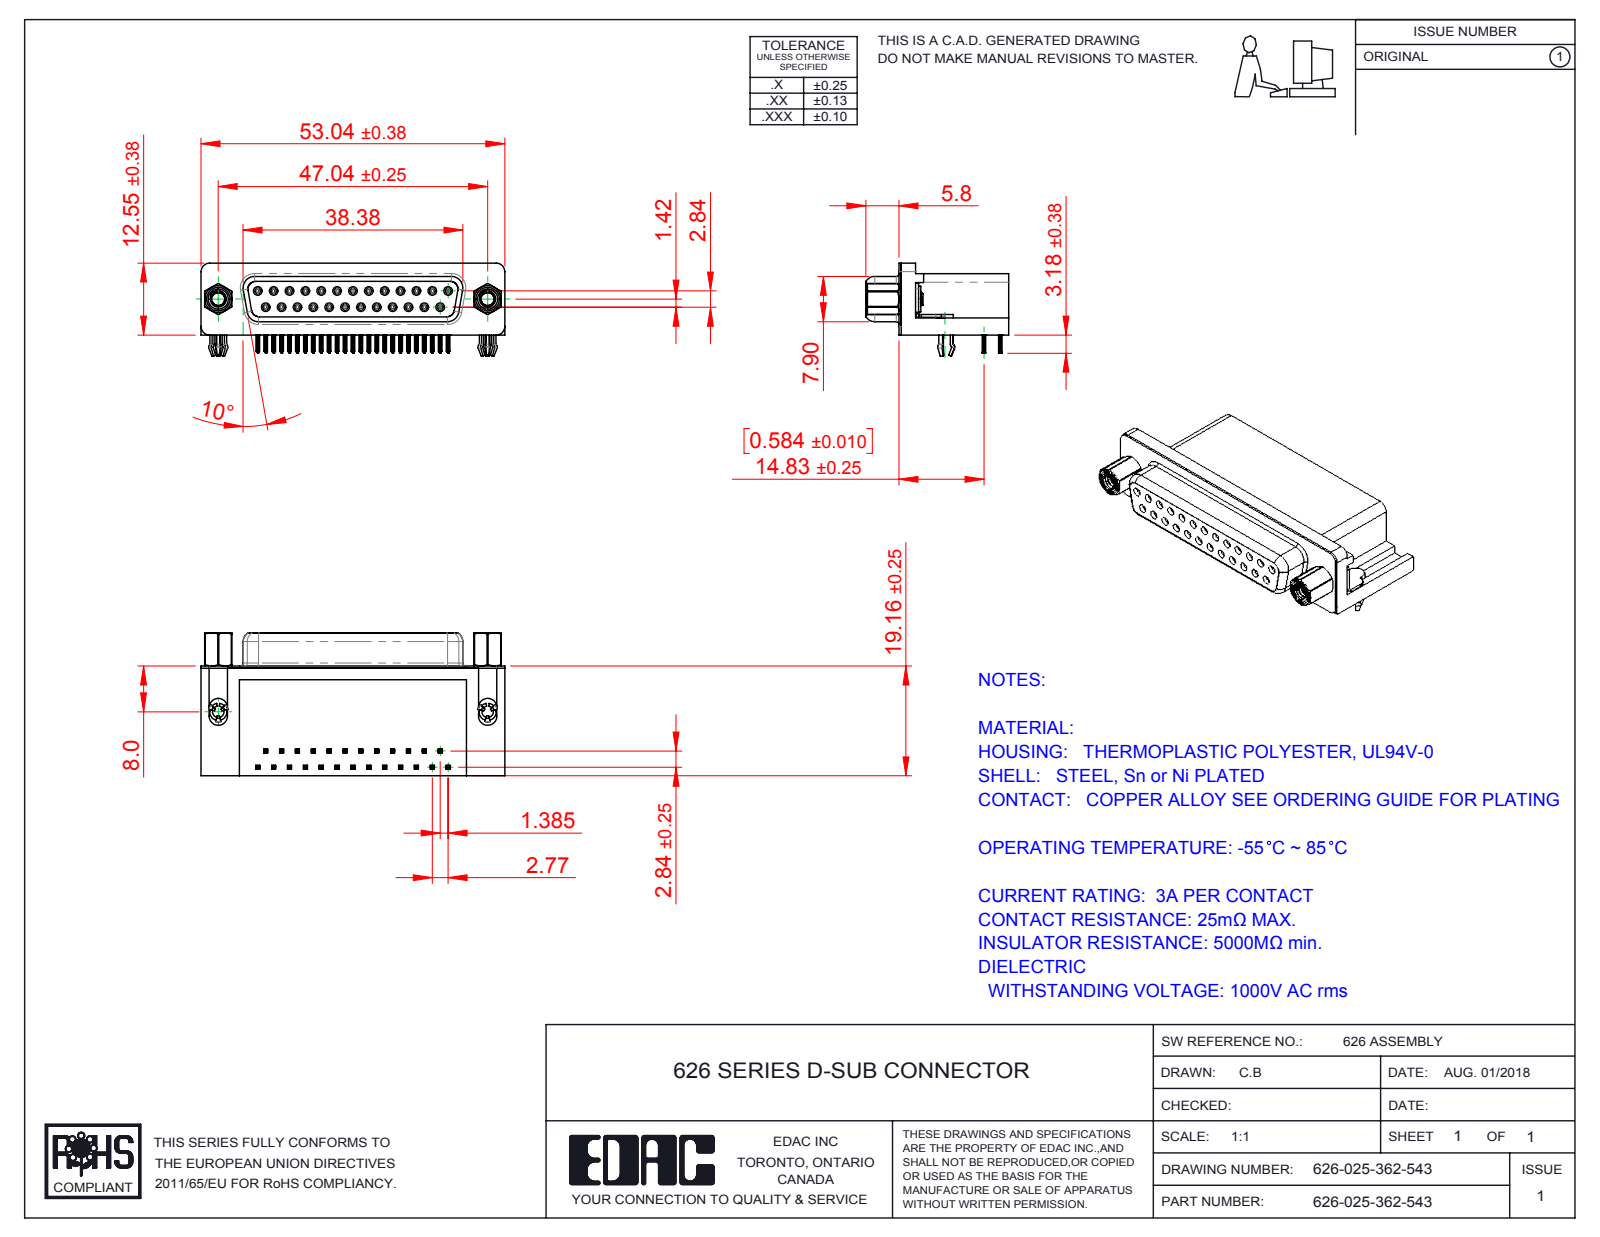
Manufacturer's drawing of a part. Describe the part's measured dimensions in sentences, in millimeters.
The part is named "626 4-40 Hex Standoff 5; 626 Shell_25 Socket; 626 Round Threaded Standoff; 626 Contact Bottom (+4 more)". Its 3-D file was written by "SolidWorks 2016 (CONFIG_CONTROL_DESIGN)". It is 33 solids with 4074 faces: 1774 planar, 1006 cylindrical and 1294 other. Overall it measures 53.04 by 24.96 by 16.25 millimeters. Its volume is 10 981 cubic millimeters and its surface area 12 108 square millimeters. Round holes: 25 of diameter 0.8, 25 of diameter 0.9, 2 of diameter 2, 2 of diameter 2.29, 2 of diameter 2.3, 2 of diameter 3.1, 2 of diameter 4, 2 of diameter 4.8, 2 of diameter 5. Round bosses or shafts: 25 of diameter 1.2, 2 of diameter 4.9, 2 of diameter 4.7, 2 of diameter 4.5, 2 of diameter 3.85, 2 of diameter 3, 2 of diameter 2.79. Partial cylindrical surfaces (rounded edges, fillets, slot ends): 200 of radius 0.1, 100 of radius 0.15, 50 of radius 0.35, 25 of radius 0.34, 18 of radius 1, 12 of radius 0.28, 8 of radius 1.35, 8 of radius 1.6. The main face-to-face distances are 0.4, 10.35, 18.76, 2.73, 6.2, 9.38, 3.18, 0.85, 2.84, 0.35. The hole center spacings are 3.16, 2.77, 5.54, 8.31, 11.08, 5.03, 5.04, 7.48.
